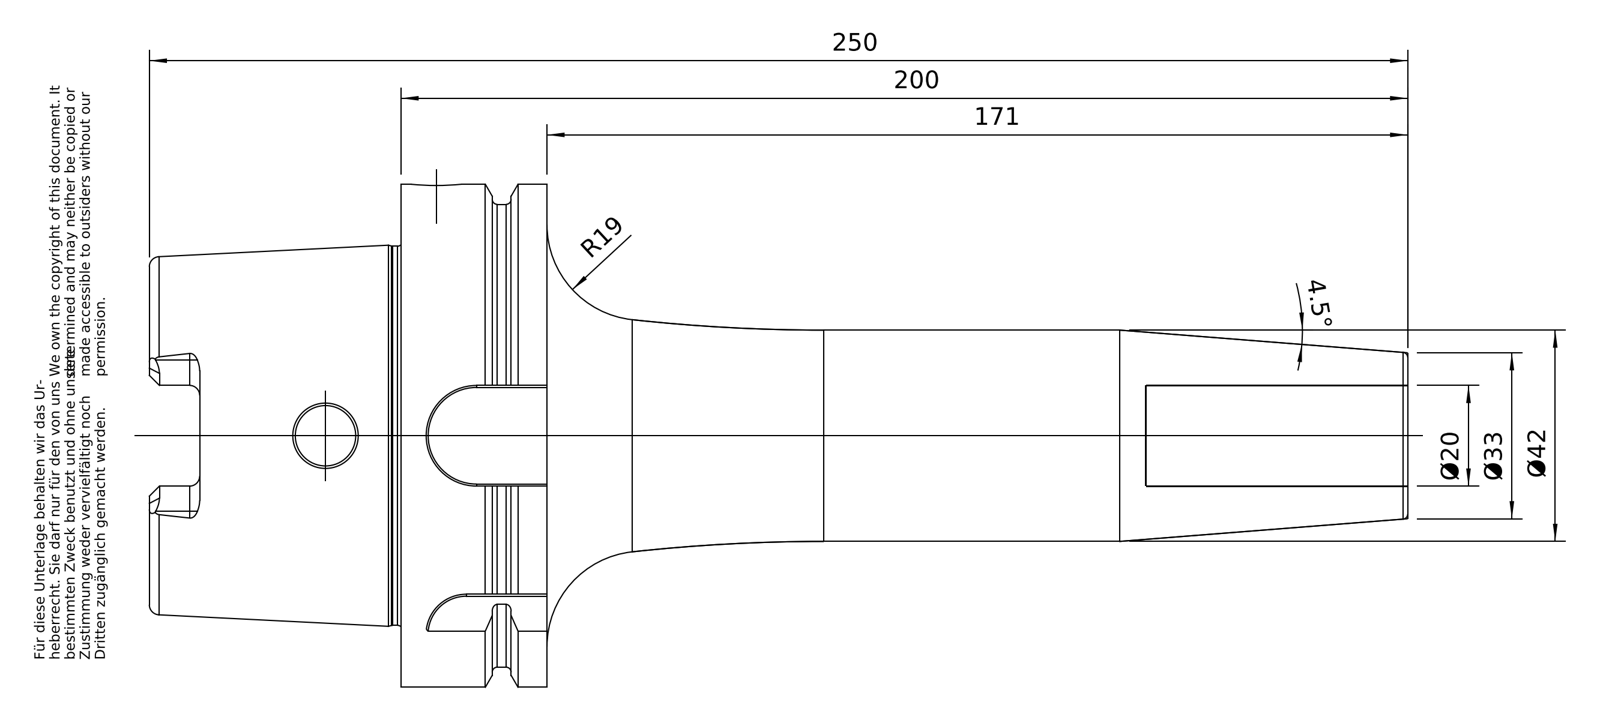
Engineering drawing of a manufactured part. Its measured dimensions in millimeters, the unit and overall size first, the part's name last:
Units: millimetres
Overall size (bounding box): 250 × 100 × 100
Round holes (diameter × count): ⌀10 ×1, ⌀12 ×1, ⌀20 ×1, ⌀22.5 ×1, ⌀24 ×1, ⌀24.32 ×1, ⌀24.5 ×1, ⌀53 ×1, ⌀63 ×1
Round bosses / shafts (diameter × count): ⌀100 ×1, ⌀92 ×1, ⌀75.36 ×1, ⌀42 ×1
Partial cylindrical surfaces — rounded edges, fillets, slot ends (radius × count): R2 ×6, R5 ×4, R8 ×1, R10 ×1, R11 ×1
Main face-to-face distances: 29, 12.5, 16.5, 50, 62.5, 79, 250, 200, 187.5, 171
Volume: 480 403 mm³ · Surface area: 73 808 mm²
Bodies: 1 solid, 176 faces (50 planar, 51 cylindrical, 75 other)
Part name (STEP PRODUCT): A100-146-20
STEP written by: PRO/ENGINEER BY PARAMETRIC TECHNOLOGY CORPORATION, 2010430 (CONFIG_CONTROL_DESIGN)
